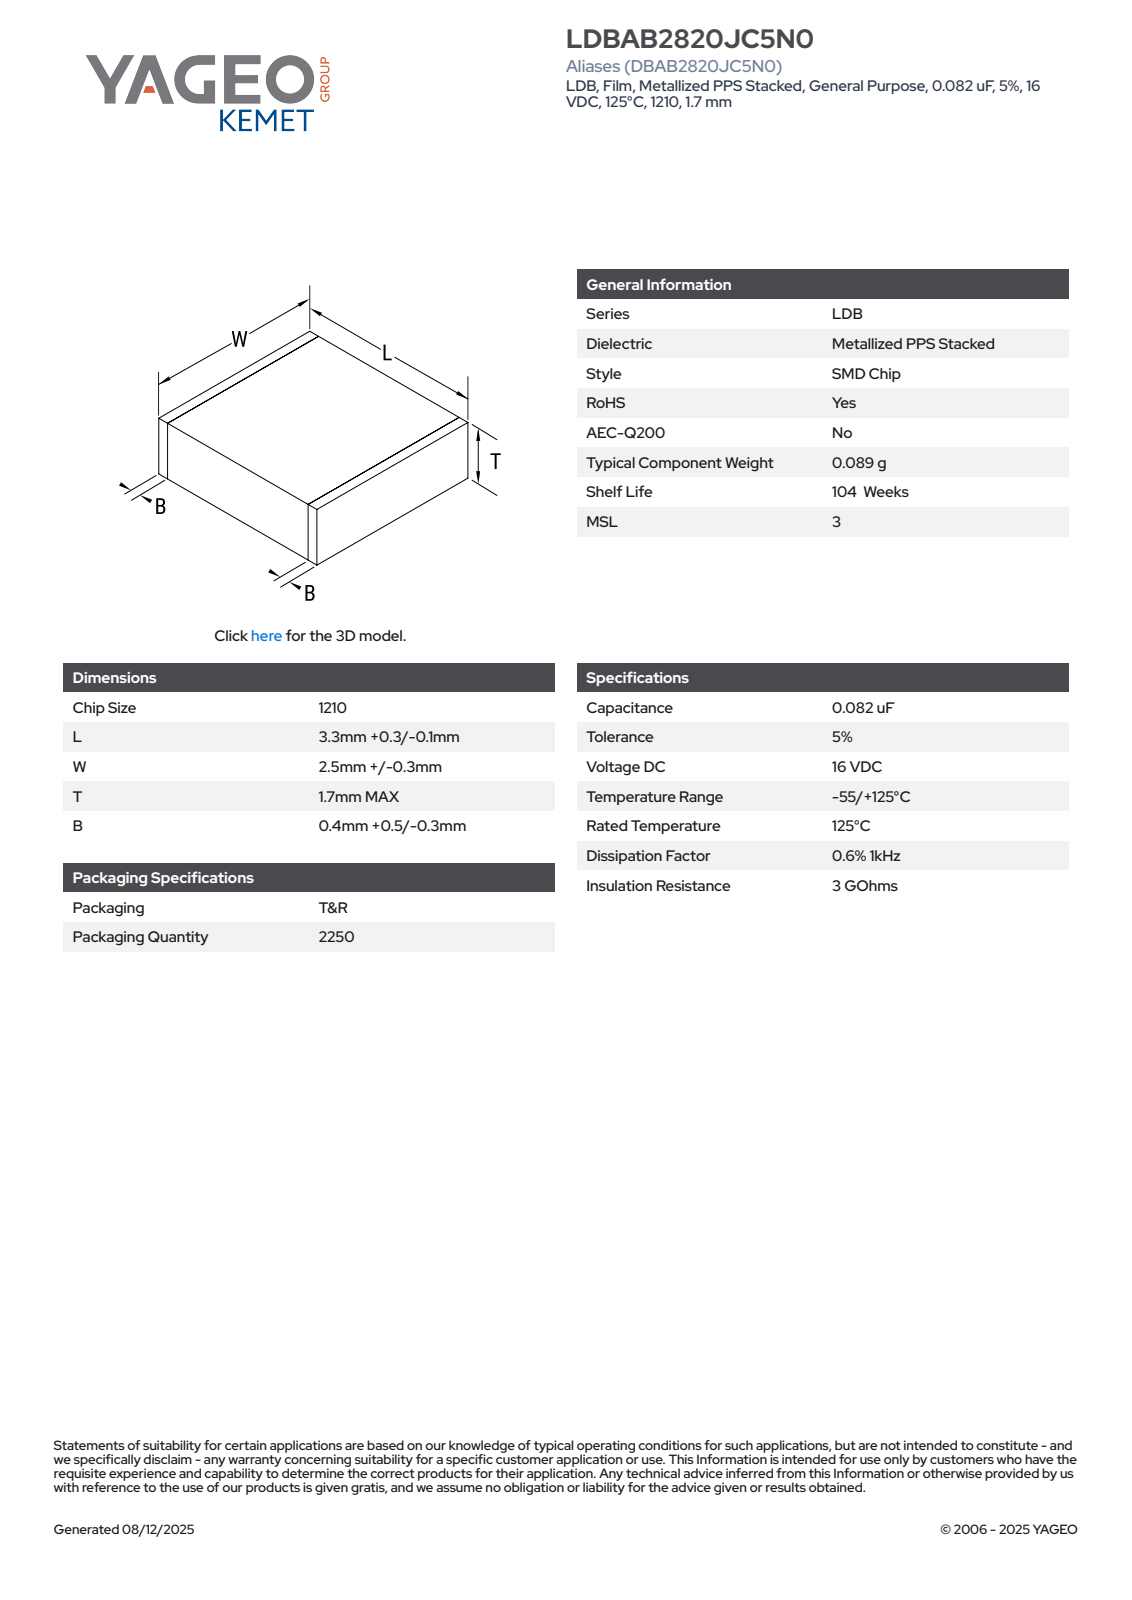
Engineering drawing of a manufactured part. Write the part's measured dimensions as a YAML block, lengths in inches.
part_name: "CFS_LDELDB_1210_L3.6W2.8T1.7B0.9"
step_written_by: "SolidWorks 2020 (AUTOMOTIVE_DESIGN)"
units: inches
bodies: {solids: 4, faces: 73, planar: 73, cylindrical: 0, other: 0}
overall_size: [0.142, 0.11, 0.067]
volume: 0.001
surface_area: 0.067
face_to_face_distances: [0.066, 0.067, 0.142, 0.109, 0.11, 0.067, 0.11, 0.02, 0.122, 0.102]
